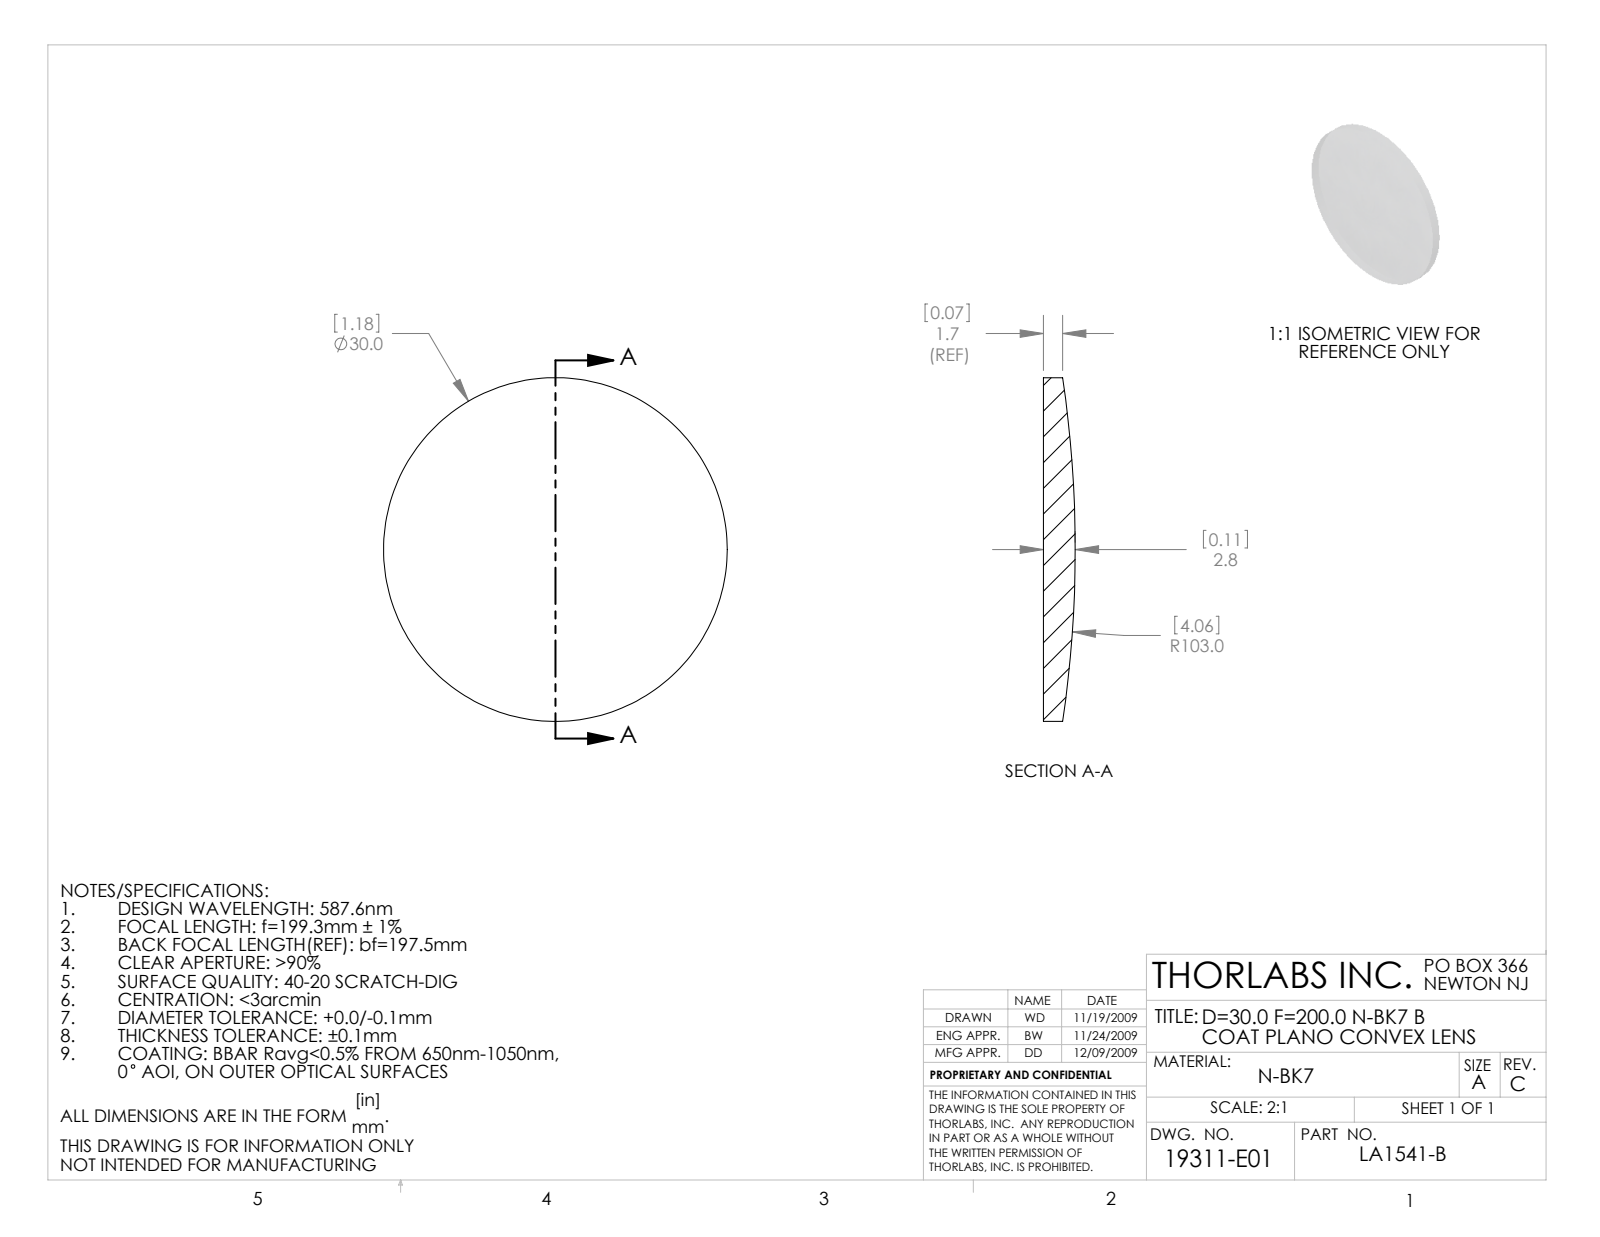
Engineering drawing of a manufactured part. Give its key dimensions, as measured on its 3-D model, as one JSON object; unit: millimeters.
{"part_name": "19311-E0W", "step_written_by": "SolidWorks 2009 (AUTOMOTIVE_DESIGN)", "units": "millimeters", "bodies": {"solids": 1, "faces": 5, "planar": 1, "cylindrical": 2, "other": 2}, "overall_size": [30, 30, 2.78], "volume_mm3": 1578, "surface_area_mm2": 1576, "round_bosses_or_shafts": [[30, 1]]}
